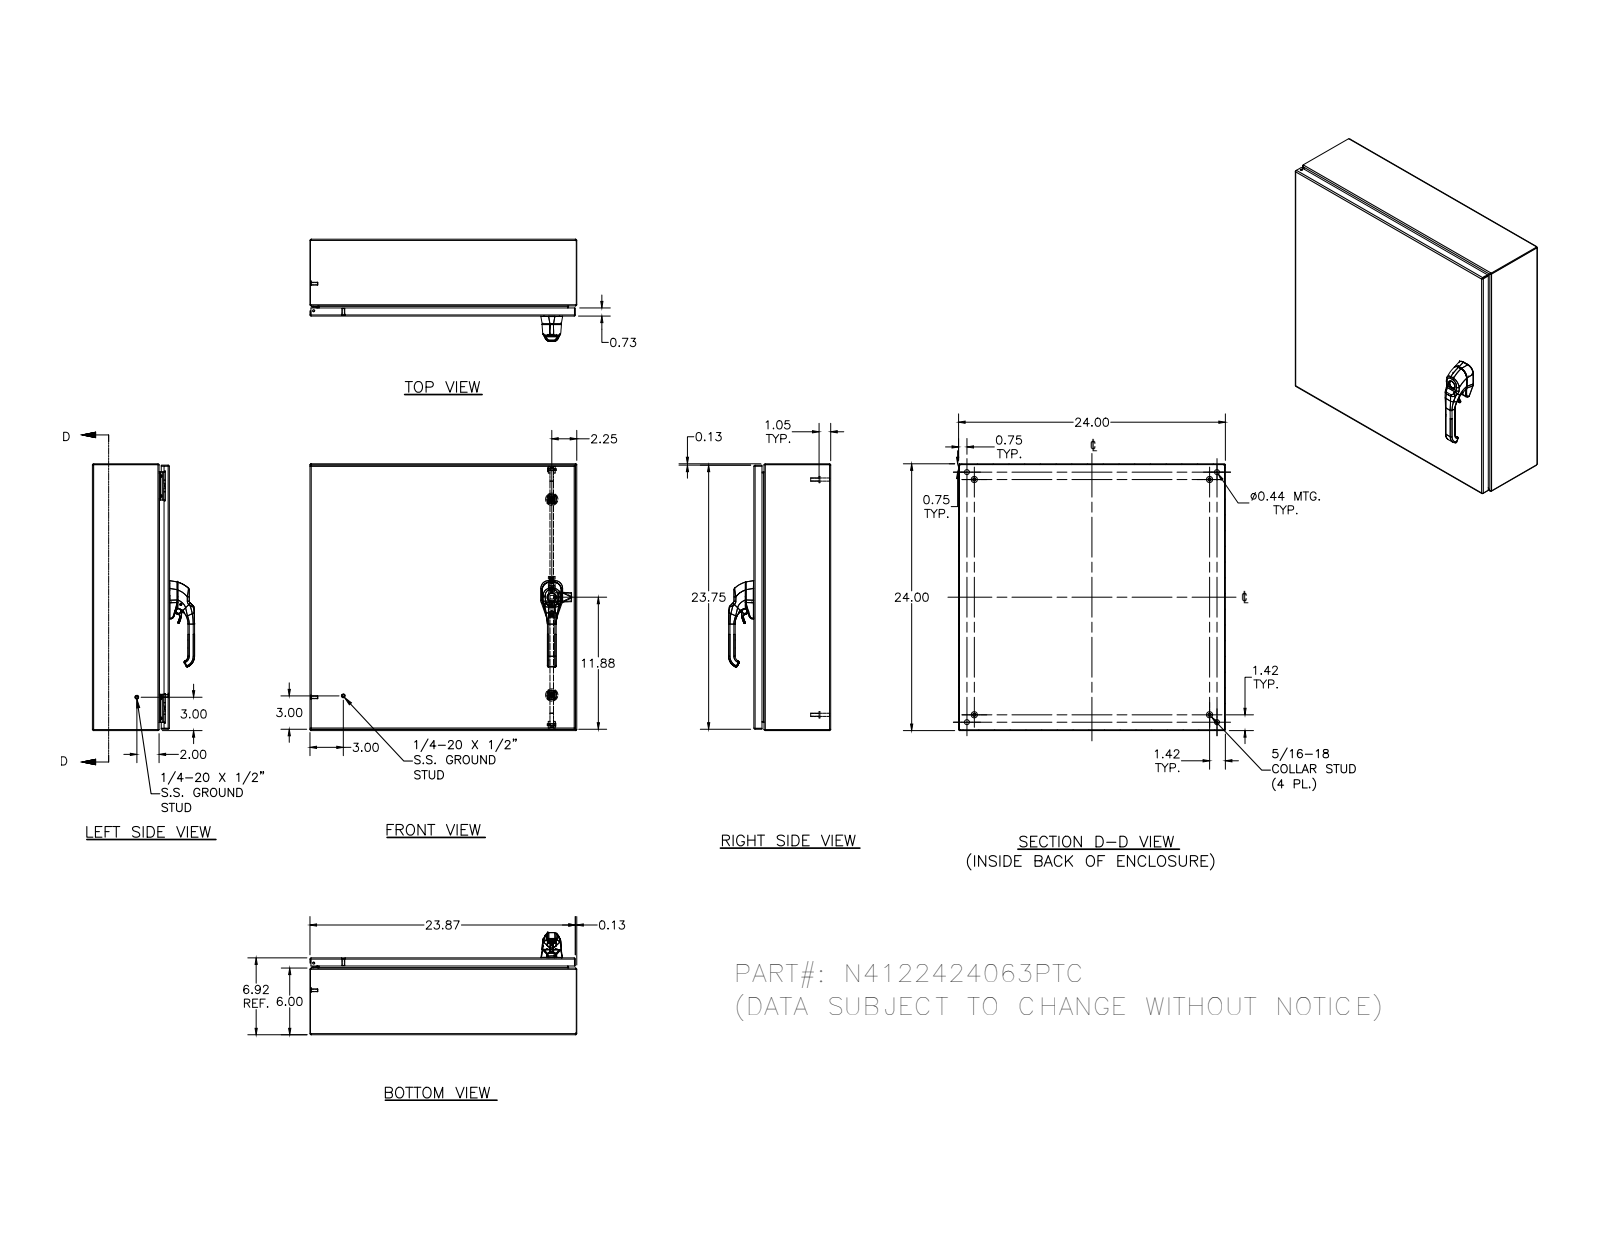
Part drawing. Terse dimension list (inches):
name: N4122424063PTC
written by: SolidWorks 2018 (AUTOMOTIVE_DESIGN)
unit: in
bodies: 51 solids, 1644 faces (589 planar, 592 cylindrical, 463 other)
size: 24 × 24 × 9.095
volume: 155.4 in³; area: 3 951 in²
holes: 5× ⌀0.188, 4× ⌀0.093, 4× ⌀0.152, 4× ⌀0.165, 4× ⌀0.167, 4× ⌀0.172, 4× ⌀0.197, 4× ⌀0.437, 2× ⌀0.106, 2× ⌀0.156, 2× ⌀0.16, 2× ⌀0.169
bosses: 10× ⌀0.25, 4× ⌀0.563, 4× ⌀0.36, 4× ⌀0.32, 4× ⌀0.3, 4× ⌀0.275, 4× ⌀0.256, 4× ⌀0.236
rounds: 30× R0.031, 26× R0.05, 20× R0.105, 18× R0.016, 18× R0.02, 16× R0.118, 14× R0.125, 8× R0.032
face distances: 0.074, 6.843, 6.917, 6.769, 23.926, 23.852, 24, 5.926, 0.917, 23.187
hole spacings: 19.996, 22.5, 22.869, 0.017, 0.66, 20.656, 0.019, 0.5
